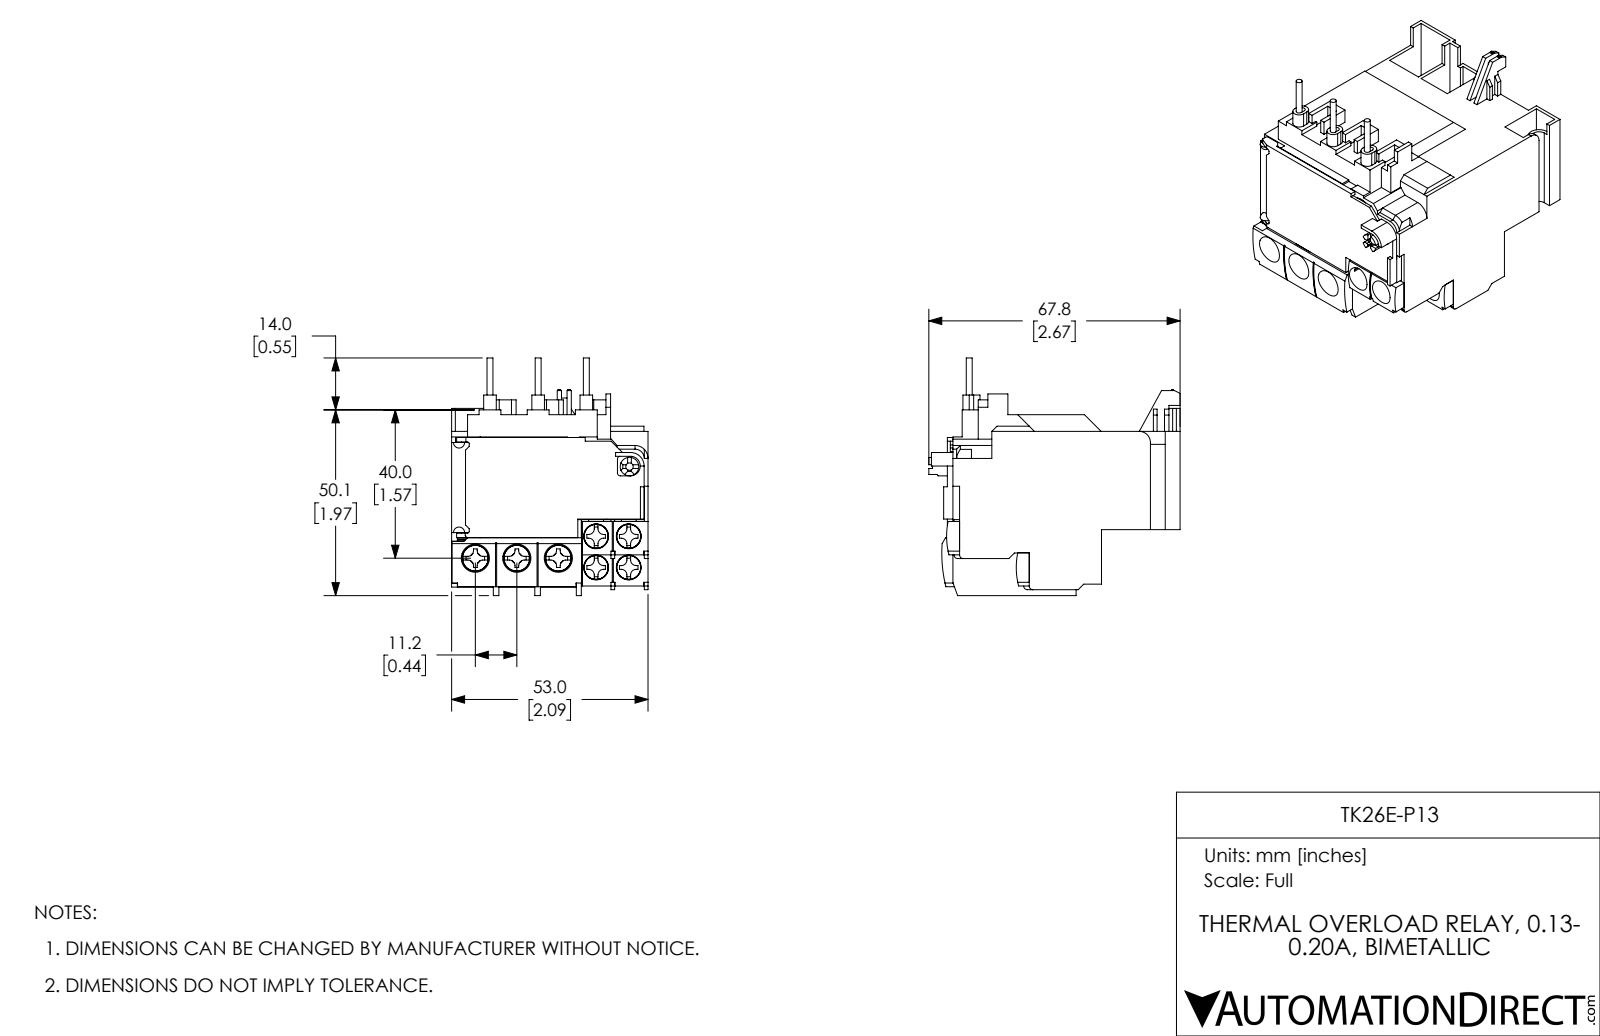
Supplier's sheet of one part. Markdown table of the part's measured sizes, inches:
| quantity | value |
| --- | --- |
| part name | TK26E-P13 |
| STEP written by | SolidWorks 2017 (AUTOMOTIVE_DESIGN) |
| units | inches |
| bodies | 38 solids, 1480 faces (1225 planar, 220 cylindrical, 35 other) |
| overall size | 2.669 × 2.524 × 2.087 |
| volume | 6.099 in³ |
| surface area | 60.15 in² |
| round holes (diameter × count) | 0.138 × 4, 0.142 × 4, 0.264 × 4, 0.157 × 3, 0.161 × 3, 0.299 × 3, 0.039 × 1, 0.079 × 1, 0.197 × 1, 0.433 × 1 |
| round bosses / shafts (diameter × count) | 0.26 × 4, 0.063 × 3, 0.236 × 1 |
| partial cylindrical surfaces (radius × count) | 0.059 × 28, 0.039 × 8, 0.02 × 6, 0.067 × 6, 0.031 × 5, 0.047 × 4, 0.171 × 4, 0.189 × 3 |
| main face-to-face distances | 0.039, 0.354, 0.059, 0.472, 2.087, 0.079, 0.394, 0.433, 0.343, 0.028 |
| hole center spacings | 0.331, 0.346, 0.441, 0.479, 0.376, 0.413, 0.464, 0.74 |
